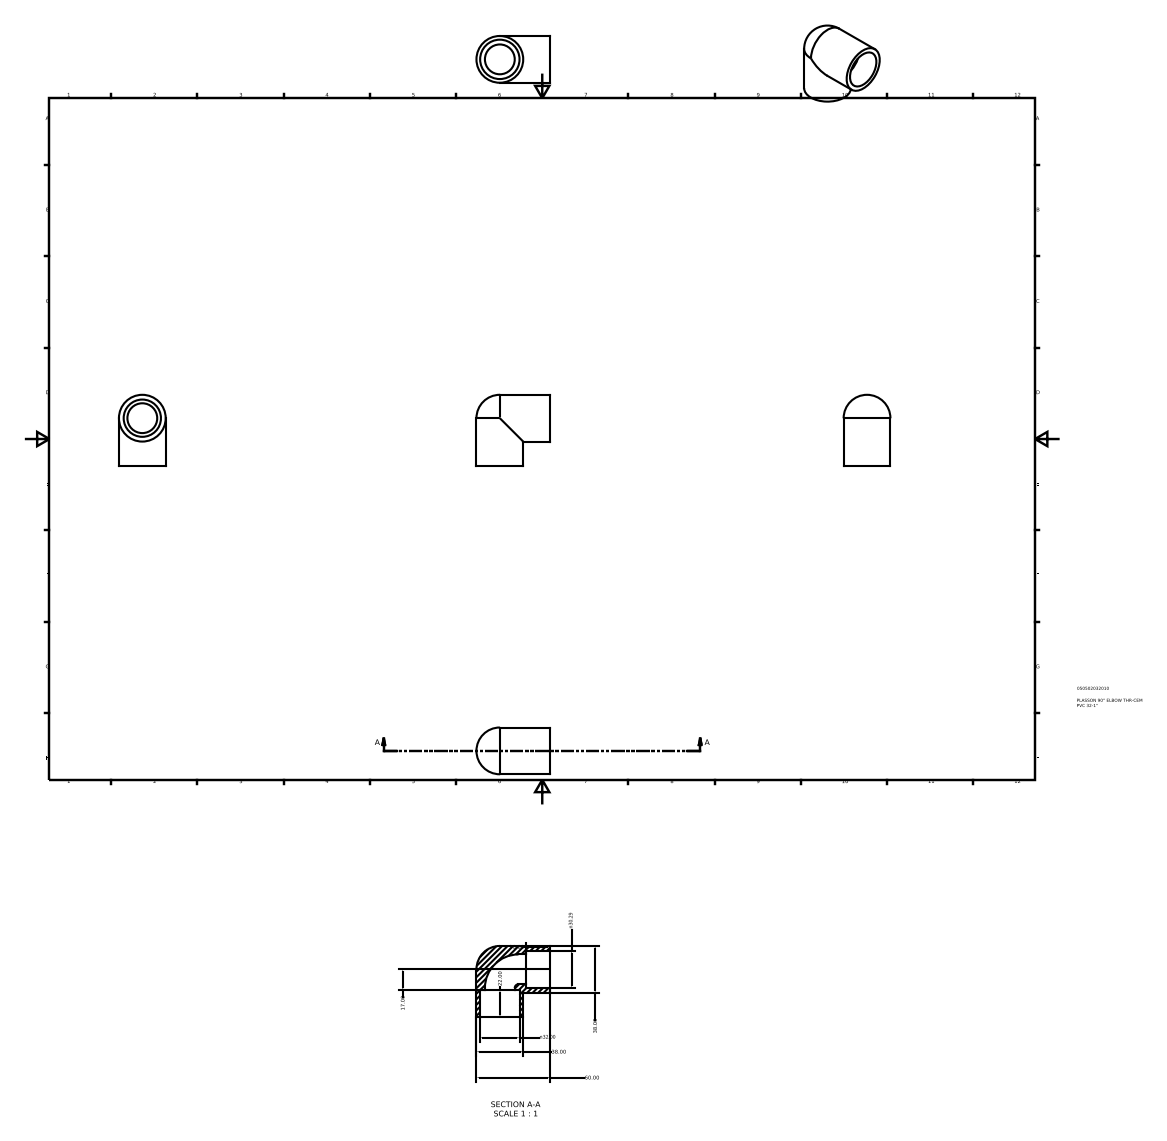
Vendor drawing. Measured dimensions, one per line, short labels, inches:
name: 050502032010
written by: Autodesk Inventor 2015 (AUTOMOTIVE_DESIGN)
unit: in
bodies: 1 solid, 12 faces (4 planar, 6 cylindrical, 2 other)
size: 2.362 × 2.283 × 1.496
volume: 2.571 in³; area: 26.5 in²
holes: 2× ⌀0.954, 1× ⌀1.193, 1× ⌀1.26
bosses: 2× ⌀1.496
face distances: 0.866, 0.787
